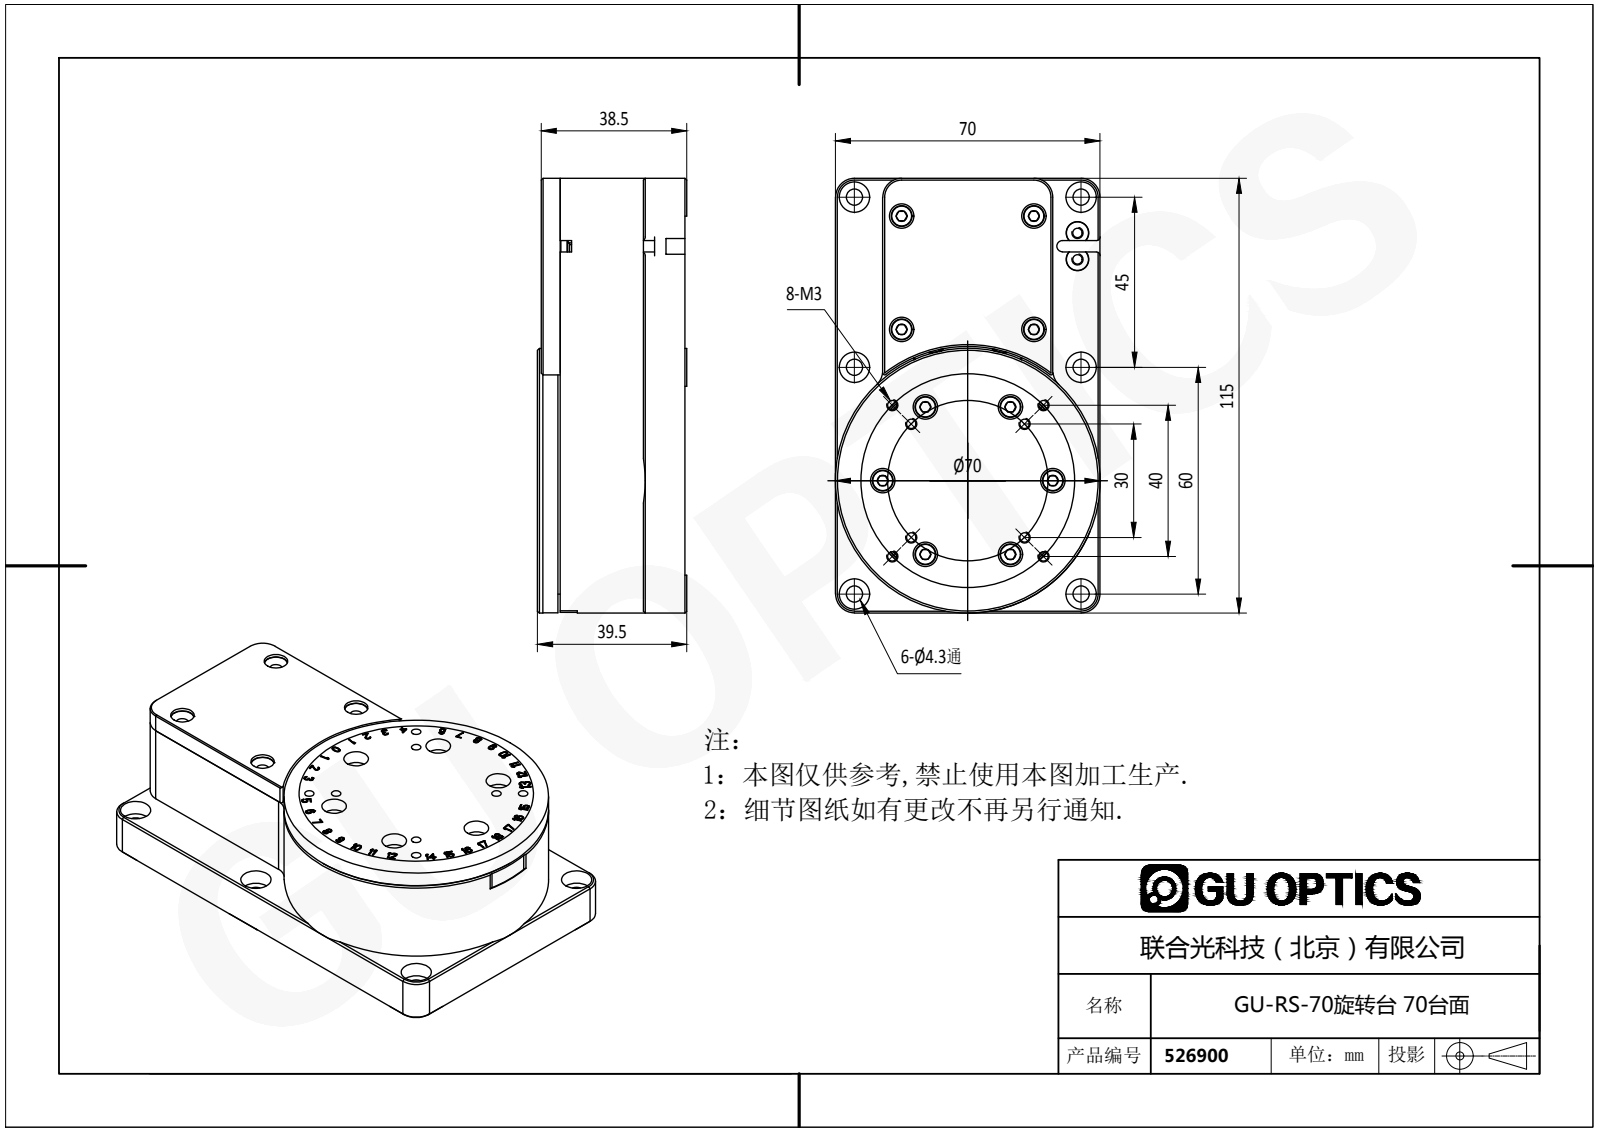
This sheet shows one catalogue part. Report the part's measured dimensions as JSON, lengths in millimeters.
{"step_written_by": "SolidWorks 2016 (CONFIG_CONTROL_DESIGN)", "units": "millimeters", "bodies": {"solids": 0, "faces": 2233, "planar": 1654, "cylindrical": 350, "other": 229}, "overall_size": [115, 70, 39.4], "round_holes": [[2.5, 28], [2.05, 12], [3, 10], [3.2, 10], [4.3, 6], [6.5, 6], [8, 6], [6.2, 4], [1.6, 2], [25, 1], [34, 1], [35.5, 1]], "round_bosses_or_shafts": [[3, 24], [2.5, 12], [2.46, 6], [2, 2], [70, 1], [61, 1], [49, 1]], "partial_cylinders_radius": [[3, 15], [2, 8], [5, 8], [0.5, 4], [1.5, 3], [1, 2], [7.9, 2], [12.1, 2]], "face_to_face_distances": [5, 6, 9, 14, 38.9, 33, 19, 8, 1, 0.5], "hole_center_spacings": [22.5, 21.21, 30, 35.36, 47.43, 50.99, 20.16, 42.43]}
